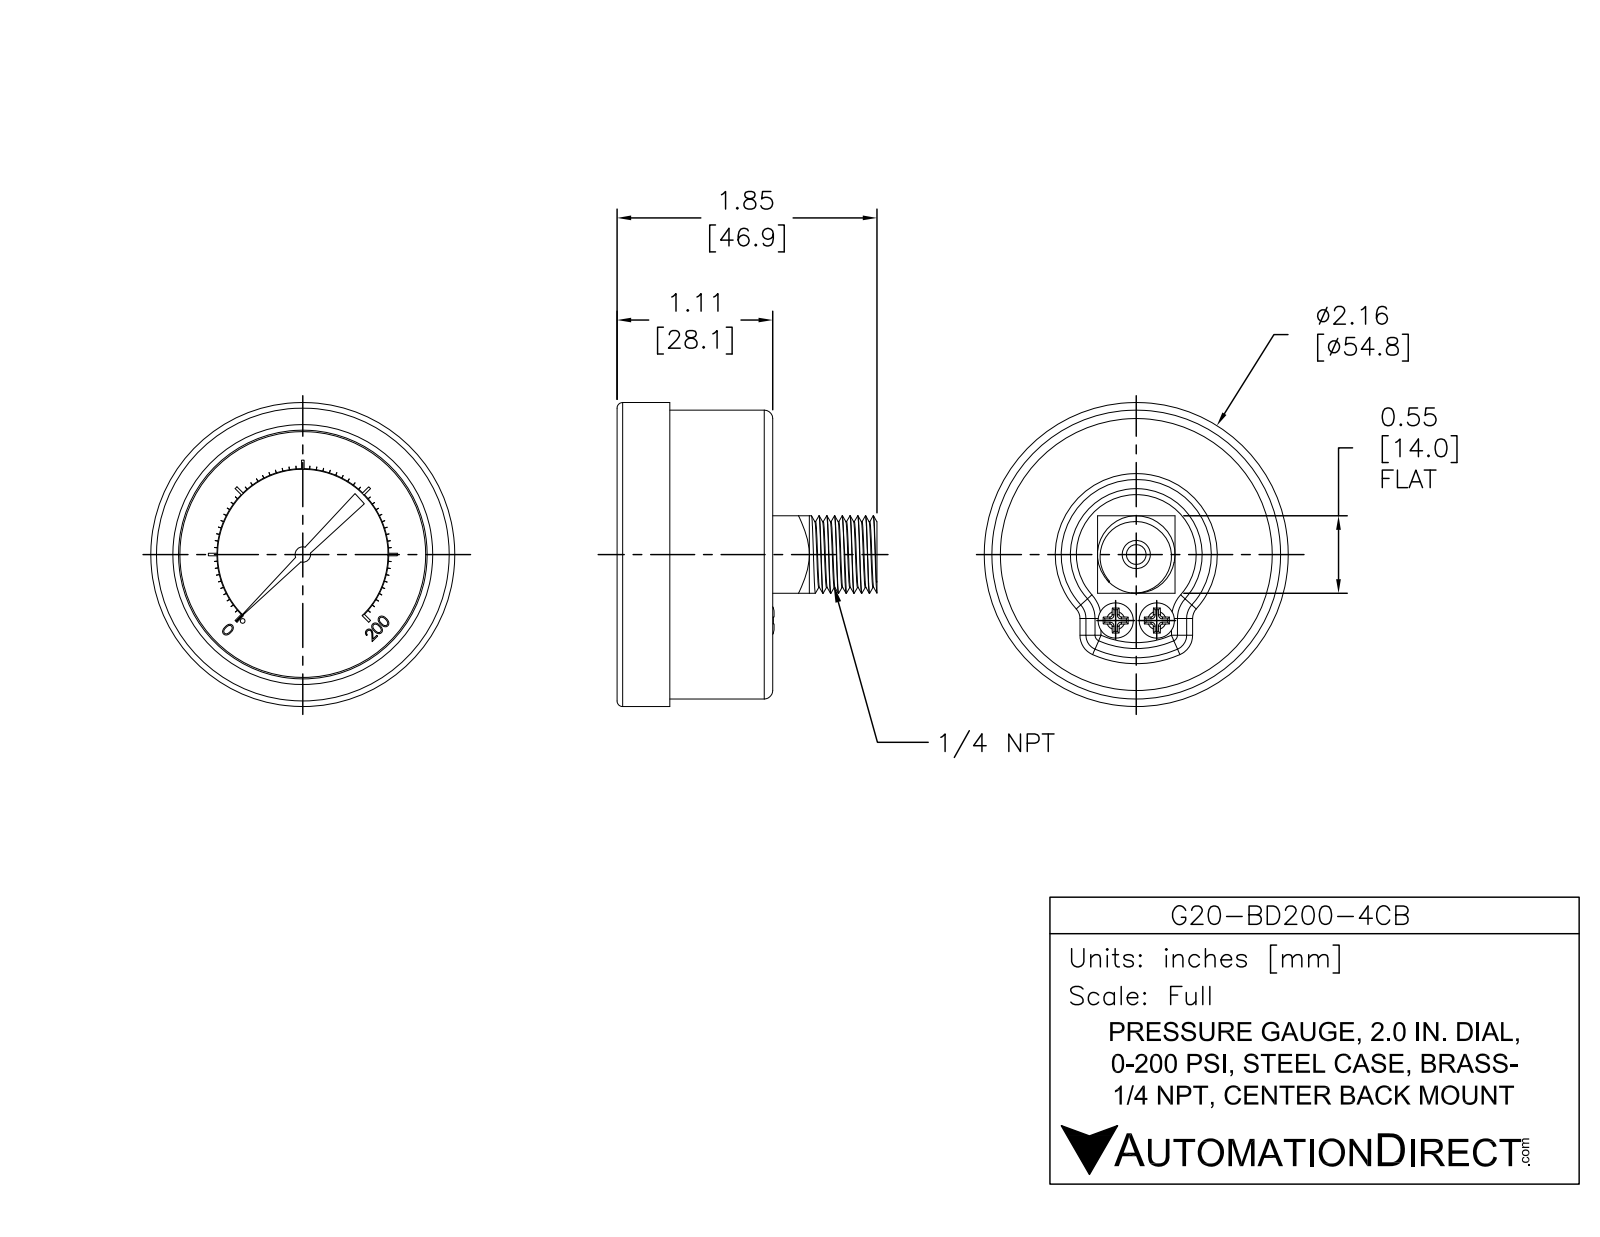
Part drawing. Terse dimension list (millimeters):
name: G20-BD200-4CB
written by: SolidWorks 2021 (AUTOMOTIVE_DESIGN)
unit: mm
bodies: 1 solid, 380 faces (240 planar, 70 cylindrical, 70 other)
size: 54.8 × 54.8 × 46.9
volume: 52 450 mm³; area: 11 720 mm²
holes: 1× ⌀3.6, 1× ⌀44.3
bosses: 2× ⌀6.4, 1× ⌀54.8, 1× ⌀52.1, 1× ⌀14, 1× ⌀2.8, 1× ⌀2.6, 1× ⌀1.4
rounds: 4× R1.5, 1× R15.4, 1× R15.5
face distances: 20.7, 28.1, 7.4, 18.5, 2.2, 9.5, 2.5, 25.5, 16, 18.2
